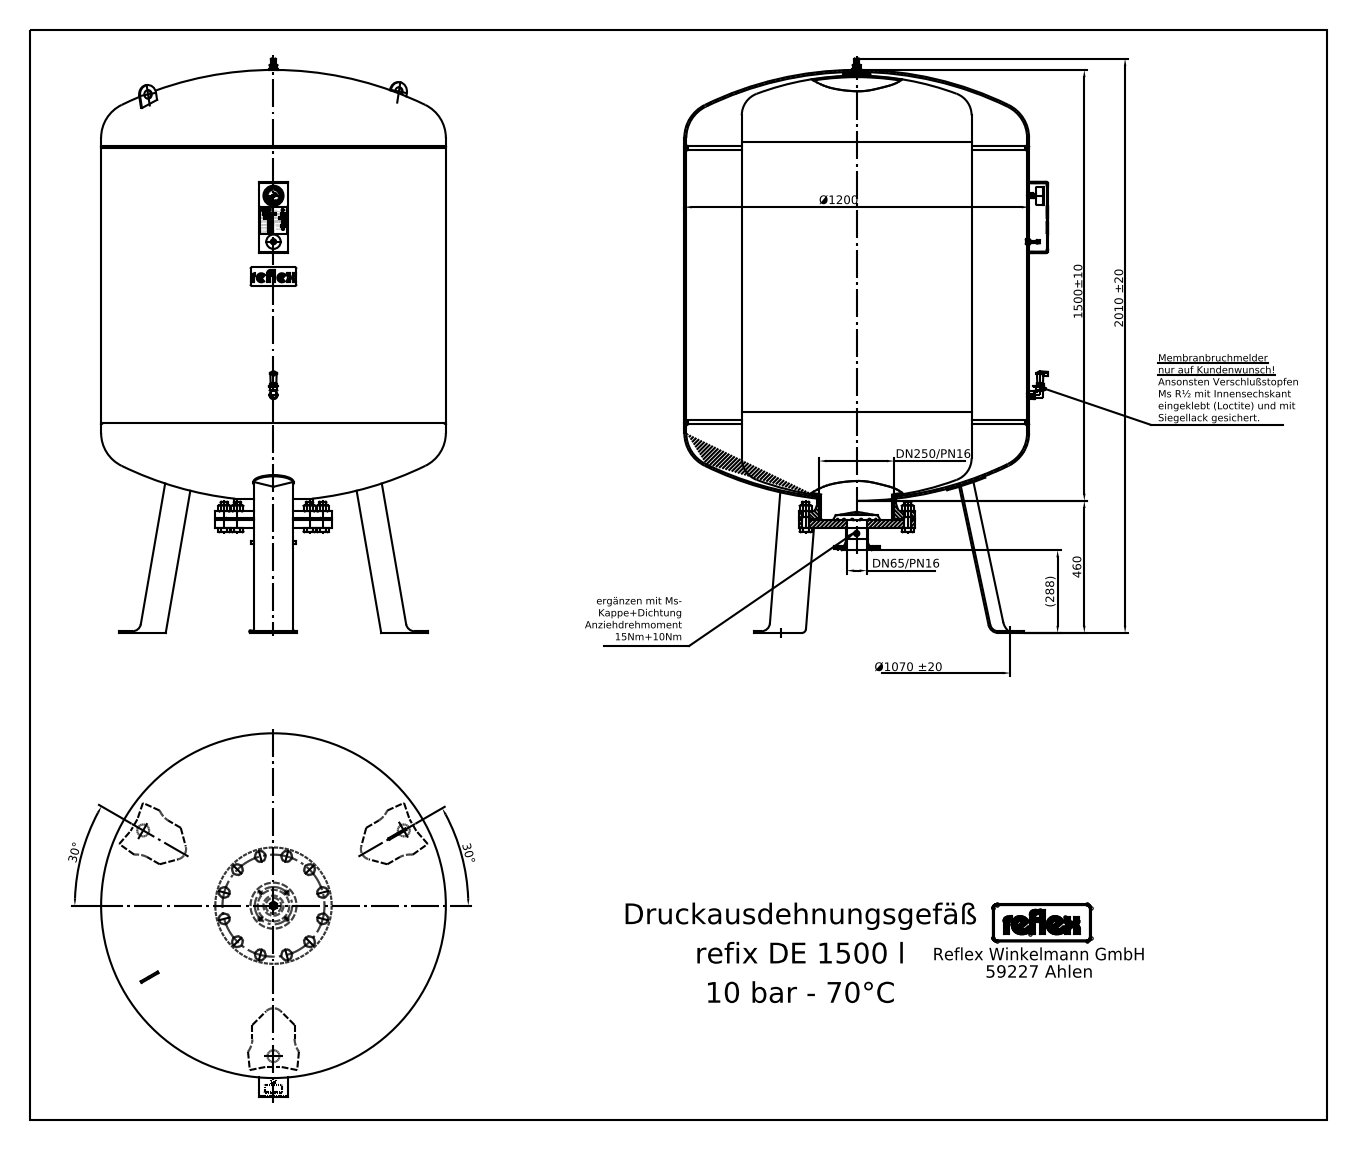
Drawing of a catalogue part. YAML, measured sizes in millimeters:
step_written_by: "Mechanical Desktop 2008 (CONFIG_CONTROL_DESIGN)"
units: millimeters
bodies: {solids: 23, faces: 612, planar: 340, cylindrical: 155, other: 117}
overall_size: [2010, 1266, 1200]
volume: 1534000000
surface_area: 13020000
round_holes:
  - {diameter: 10, count: 1}
  - {diameter: 30, count: 1}
  - {diameter: 50, count: 1}
  - {diameter: 69, count: 1}
  - {diameter: 260.4, count: 1}
round_bosses_or_shafts:
  - {diameter: 16, count: 13}
  - {diameter: 28, count: 2}
  - {diameter: 26, count: 2}
  - {diameter: 20, count: 2}
  - {diameter: 1200, count: 1}
  - {diameter: 405, count: 1}
  - {diameter: 273, count: 1}
  - {diameter: 76.1, count: 1}
partial_cylinders:
  - {radius: 25, count: 18}
  - {radius: 5.62, count: 4}
  - {radius: 2.25, count: 3}
  - {radius: 9, count: 3}
  - {radius: 1, count: 2}
  - {radius: 3.84, count: 2}
  - {radius: 5, count: 2}
  - {radius: 6.75, count: 2}
face_to_face_distances: [1000, 26, 312, 1312, 338, 1338, 31, 5.97, 5.89, 57]
hole_center_spacings: [82.33, 615.5, 620.58, 672.62]
